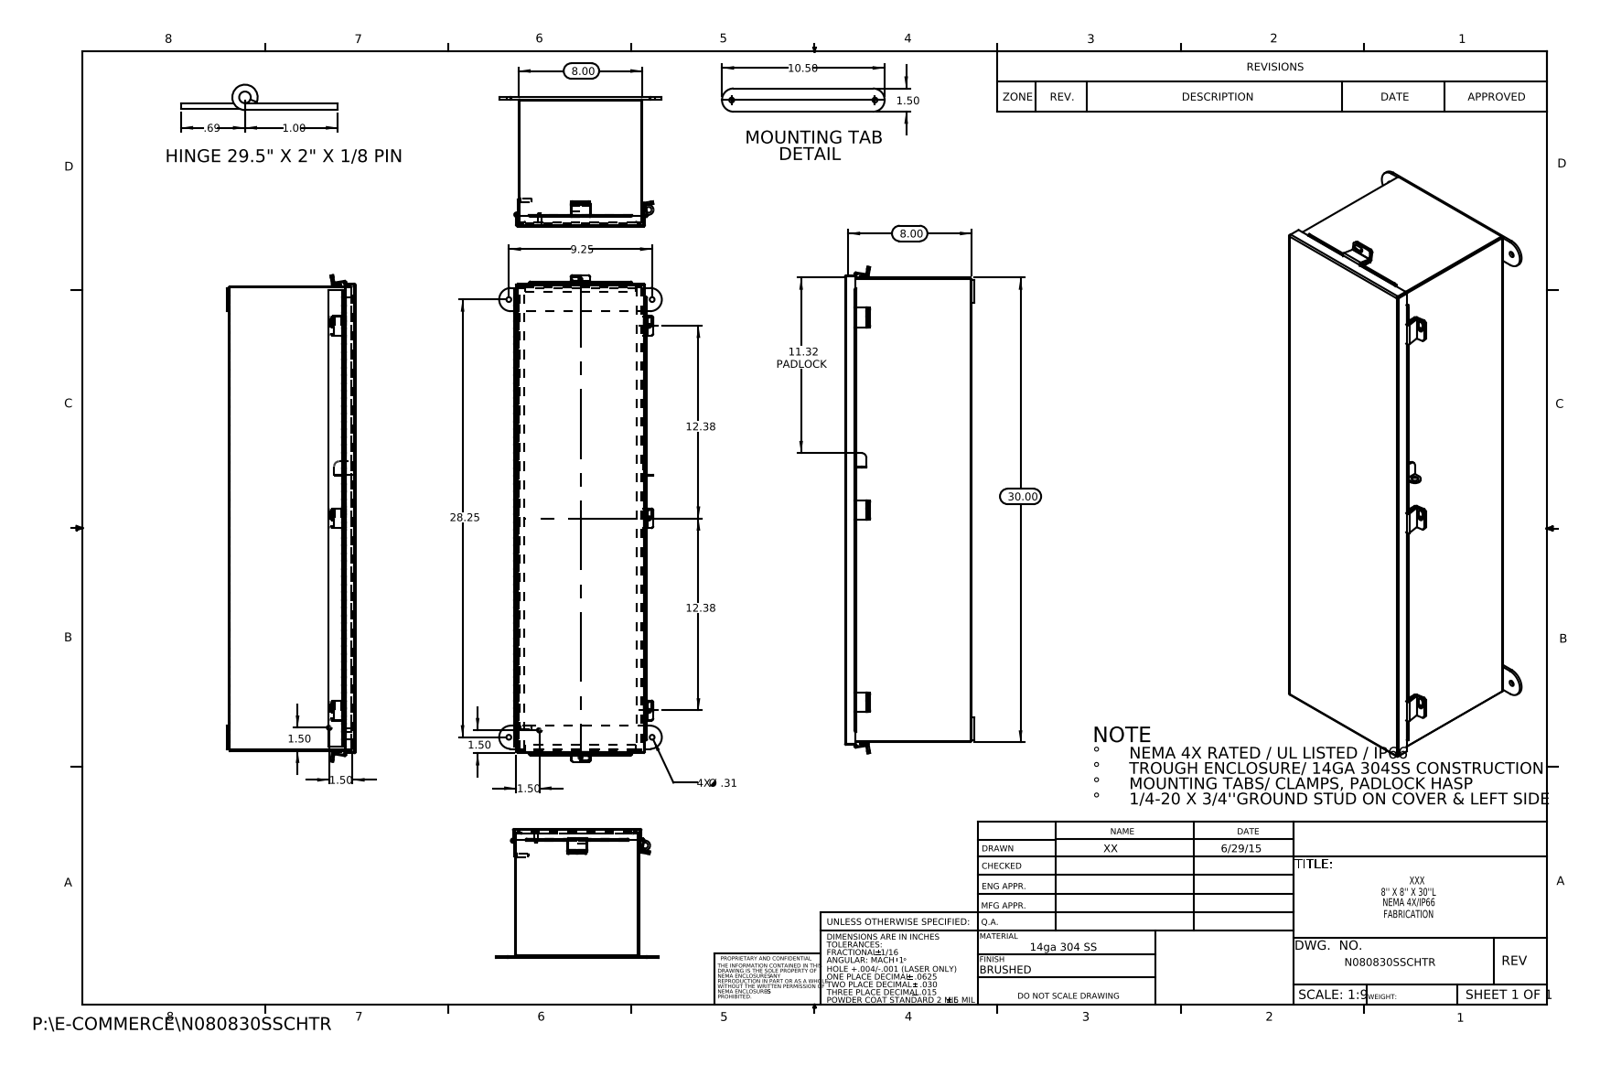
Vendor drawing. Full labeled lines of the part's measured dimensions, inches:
Part name (STEP PRODUCT): HW-CLH-JH-20154; N080830SSCHTR JIC Enclosure Template; N080830SSCHTR JIC Cover Clamp; N080830SSCHTR Hinge Cover Side JIC (+8 more)
STEP written by: SolidWorks 2015 (CONFIG_CONTROL_DESIGN)
Units: inches
Bodies: 21 solids, 994 faces (605 planar, 369 cylindrical, 20 other)
Overall size (bounding box): 31.407 × 10.5 × 8.337
Volume: 96.28 in³ · Surface area: 2 577 in²
Round holes (diameter × count): ⌀0.25 ×5, ⌀0.313 ×4, ⌀0.125 ×1, ⌀0.125 ×1, ⌀0.375 ×1
Round bosses / shafts (diameter × count): ⌀0.315 ×2, ⌀0.236 ×2, ⌀0.273 ×1, ⌀0.25 ×1
Partial cylindrical surfaces — rounded edges, fillets, slot ends (radius × count): R0.125 ×19, R0.009 ×12, R0.013 ×11, R0.088 ×11, R0.133 ×10, R0.083 ×6, R0.1 ×6, R0.75 ×4
Main face-to-face distances: 0.075, 7.925, 8.128, 8, 7.85, 8.203, 8.053, 29.925, 0.149, 8.074
Hole centre spacings: 9.25, 12.425, 28.25, 29.726, 8.541, 24.85
